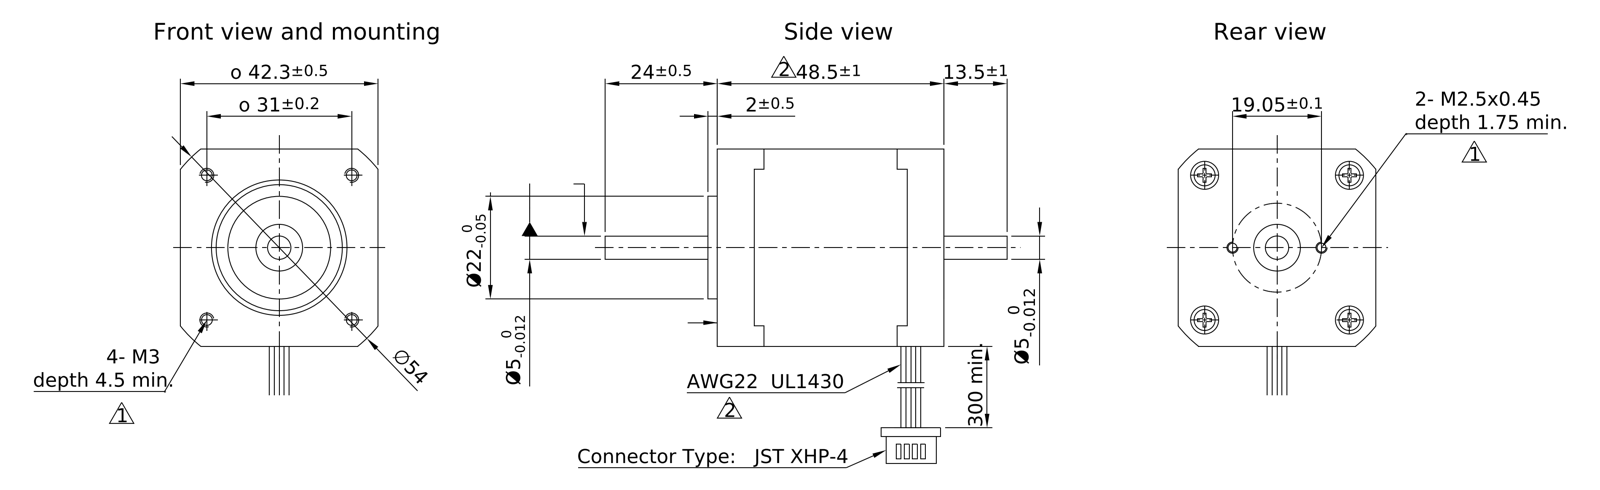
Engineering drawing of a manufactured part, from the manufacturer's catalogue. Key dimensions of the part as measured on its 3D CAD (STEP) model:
Part name (STEP PRODUCT): ST4118L..._B
STEP written by: Autodesk Inventor 2010 (AUTOMOTIVE_DESIGN)
Units: millimetres
Bodies: 0 solids, 133 faces (77 planar, 35 cylindrical, 21 other)
Overall size (bounding box): 86.5 × 54 × 42
Round holes (diameter × count): ⌀6 ×4, ⌀2.01 ×2, ⌀2.46 ×2, ⌀2.46 ×2, ⌀7.5 ×1
Round bosses / shafts (diameter × count): ⌀1 ×4, ⌀22 ×1, ⌀5 ×1
Partial cylindrical surfaces — rounded edges, fillets, slot ends (radius × count): R2 ×8, R27 ×1
Main face-to-face distances: 42, 49, 48.08, 2, 51, 11, 38, 48.5, 0.5, 2.5
Hole centre spacings: 16.61, 21.92, 29.44, 31, 9.53, 43.84, 19.06
